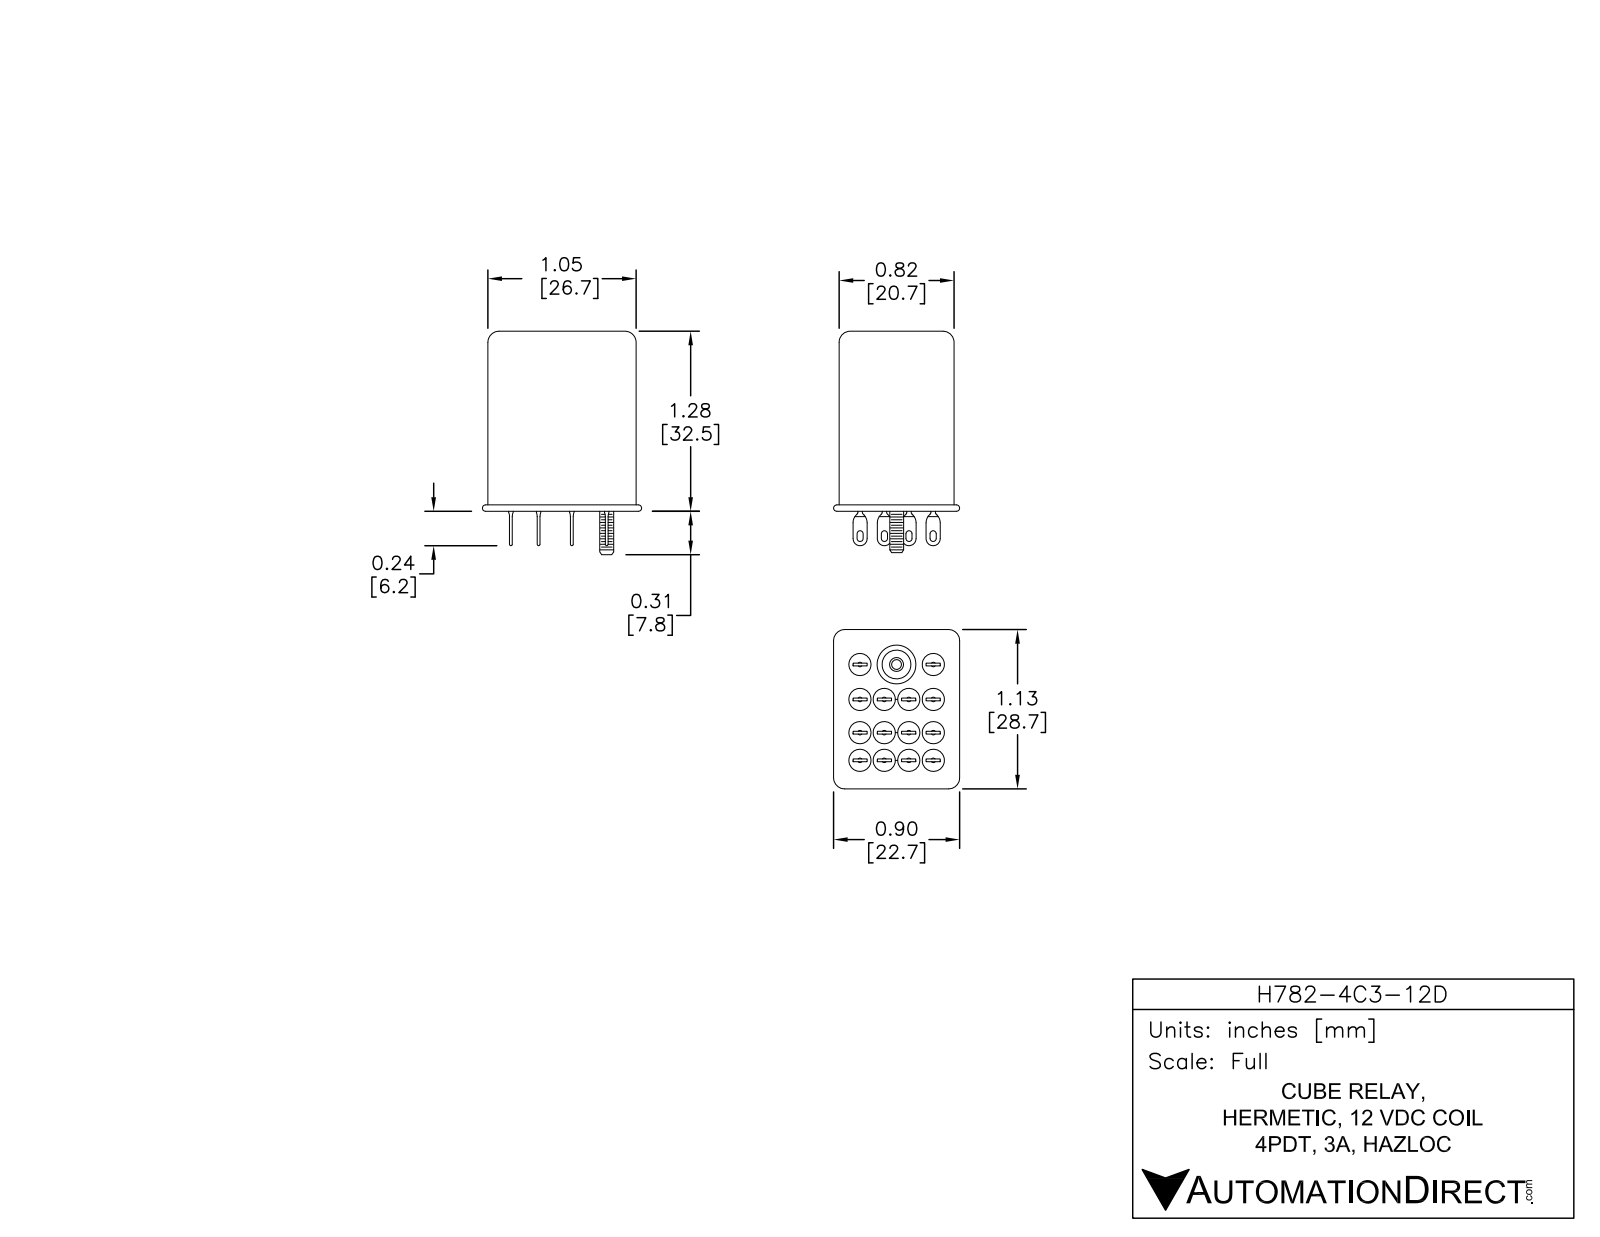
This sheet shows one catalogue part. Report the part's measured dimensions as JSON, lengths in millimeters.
{"part_name": "H782-4C3-12D", "step_written_by": "SolidWorks 2013 (AUTOMOTIVE_DESIGN)", "units": "millimeters", "bodies": {"solids": 2, "faces": 408, "planar": 186, "cylindrical": 178, "other": 44}, "overall_size": [35.12, 28.8, 22.9], "volume_mm3": 15264, "surface_area_mm2": 4133, "round_holes": [[6, 1]], "round_bosses_or_shafts": [[3.15, 14], [2.4, 1]], "partial_cylinders_radius": [[0.1, 56], [0.5, 36], [0.2, 8], [2, 4]], "face_to_face_distances": [20.5, 27.6, 26.5, 27.62, 5.2, 0.4, 10.4, 10, 4.8, 5.6]}
